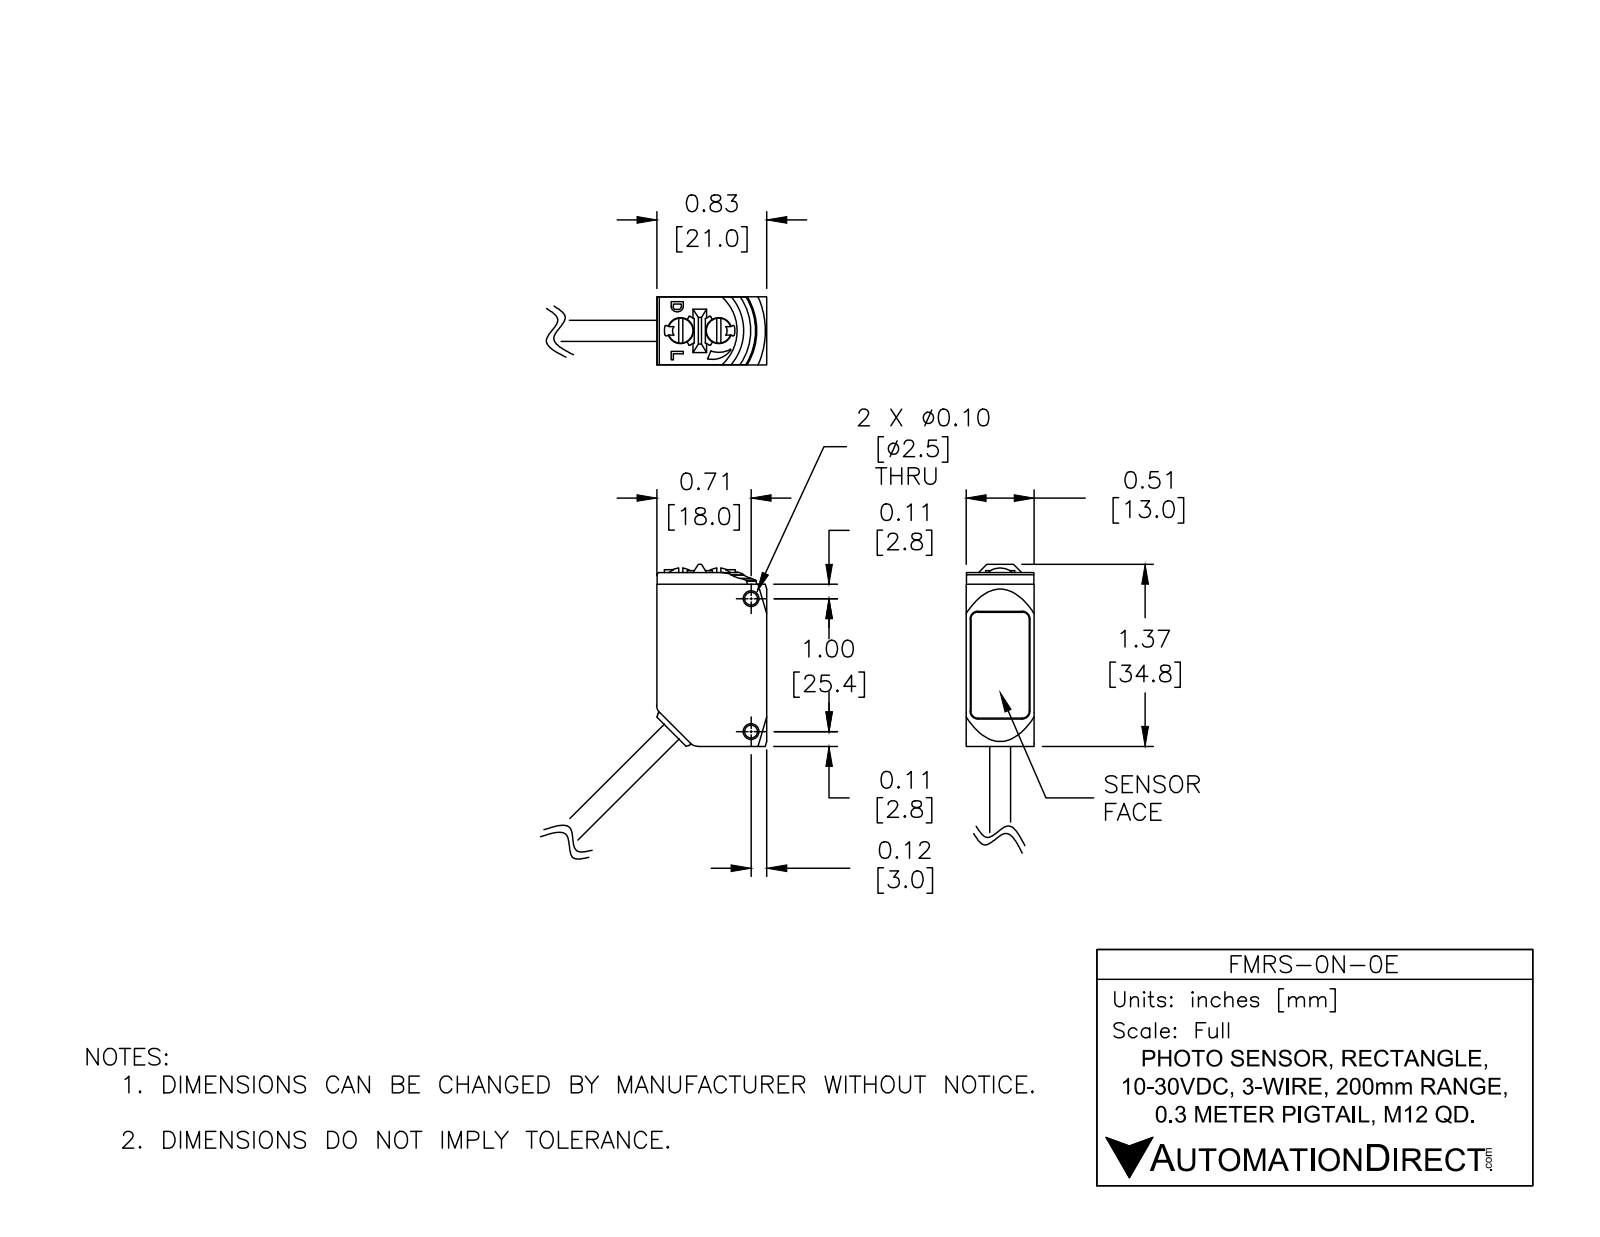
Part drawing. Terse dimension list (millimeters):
name: FMRS-0N-0E
written by: SolidWorks 2017 (AUTOMOTIVE_DESIGN)
unit: mm
bodies: 1 solid, 186 faces (89 planar, 72 cylindrical, 25 other)
size: 52.9 × 39.1 × 13
volume: 8 880 mm³; area: 3 533 mm²
holes: 2× ⌀2.5, 2× ⌀5
bosses: 2× ⌀4.8, 1× ⌀4
rounds: 7× R0.5, 7× R0.5, 4× R0.2, 4× R0.3, 4× R1.3, 4× R1.5, 3× R0.1, 2× R0.5
face distances: 13, 21, 33.2, 0.9, 13, 0.8, 12.2, 0.9, 12, 12
hole spacings: 7.3, 25.4
